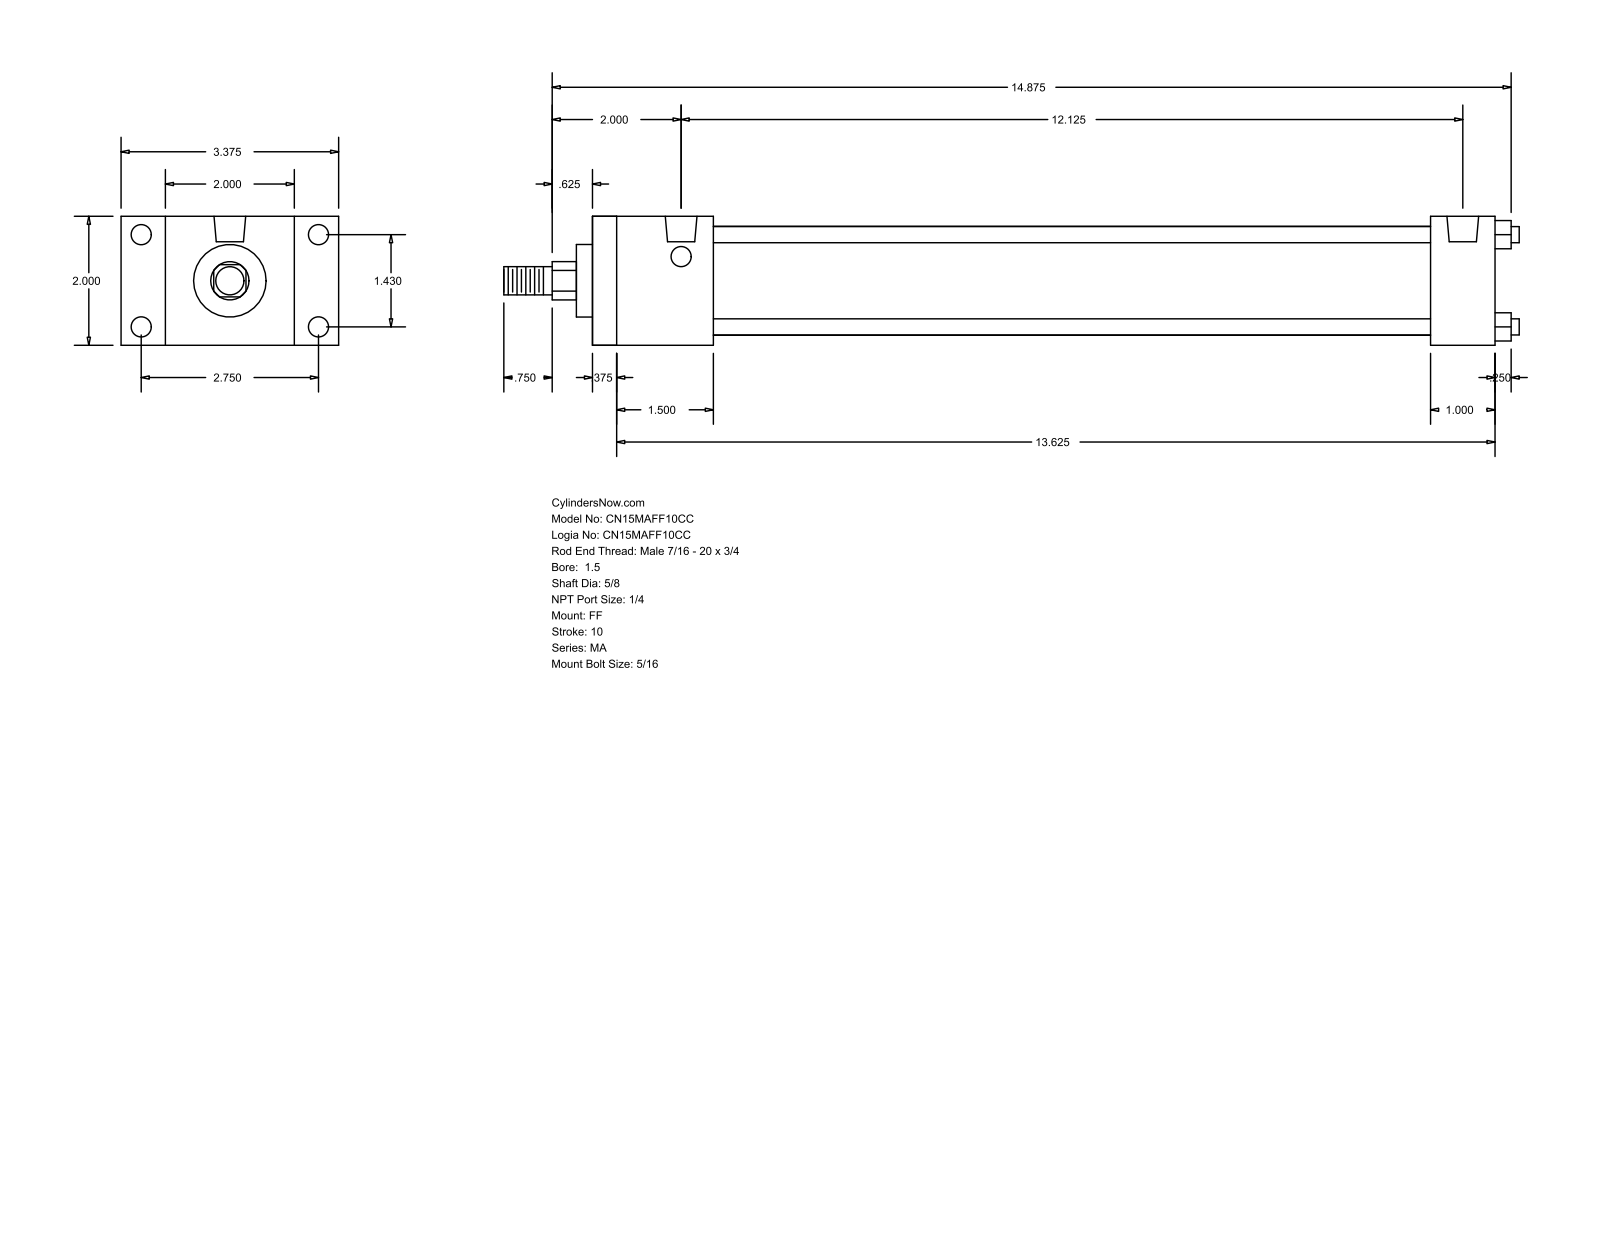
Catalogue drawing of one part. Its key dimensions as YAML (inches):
part_name: "MA_FF__0150_0.625"
step_written_by: "GSSL Pune (CONFIG_CONTROL_DESIGN)"
units: inches
bodies: {solids: 0, faces: 92, planar: 64, cylindrical: 28, other: 0}
overall_size: [15.75, 3.375, 2]
round_holes:
  - {diameter: 0.313, count: 8}
  - {diameter: 0.492, count: 2}
round_bosses_or_shafts:
  - {diameter: 0.25, count: 4}
  - {diameter: 1.69, count: 1}
  - {diameter: 1.125, count: 1}
  - {diameter: 0.625, count: 1}
  - {diameter: 0.437, count: 1}
partial_cylinders:
  - {radius: 0.297, count: 1}
face_to_face_distances: [2, 14, 0.375, 13.625, 1.875, 13, 1.5, 12.625, 11.125, 12.125]
hole_center_spacings: [1.43, 2.75, 3.099, 12.125]
